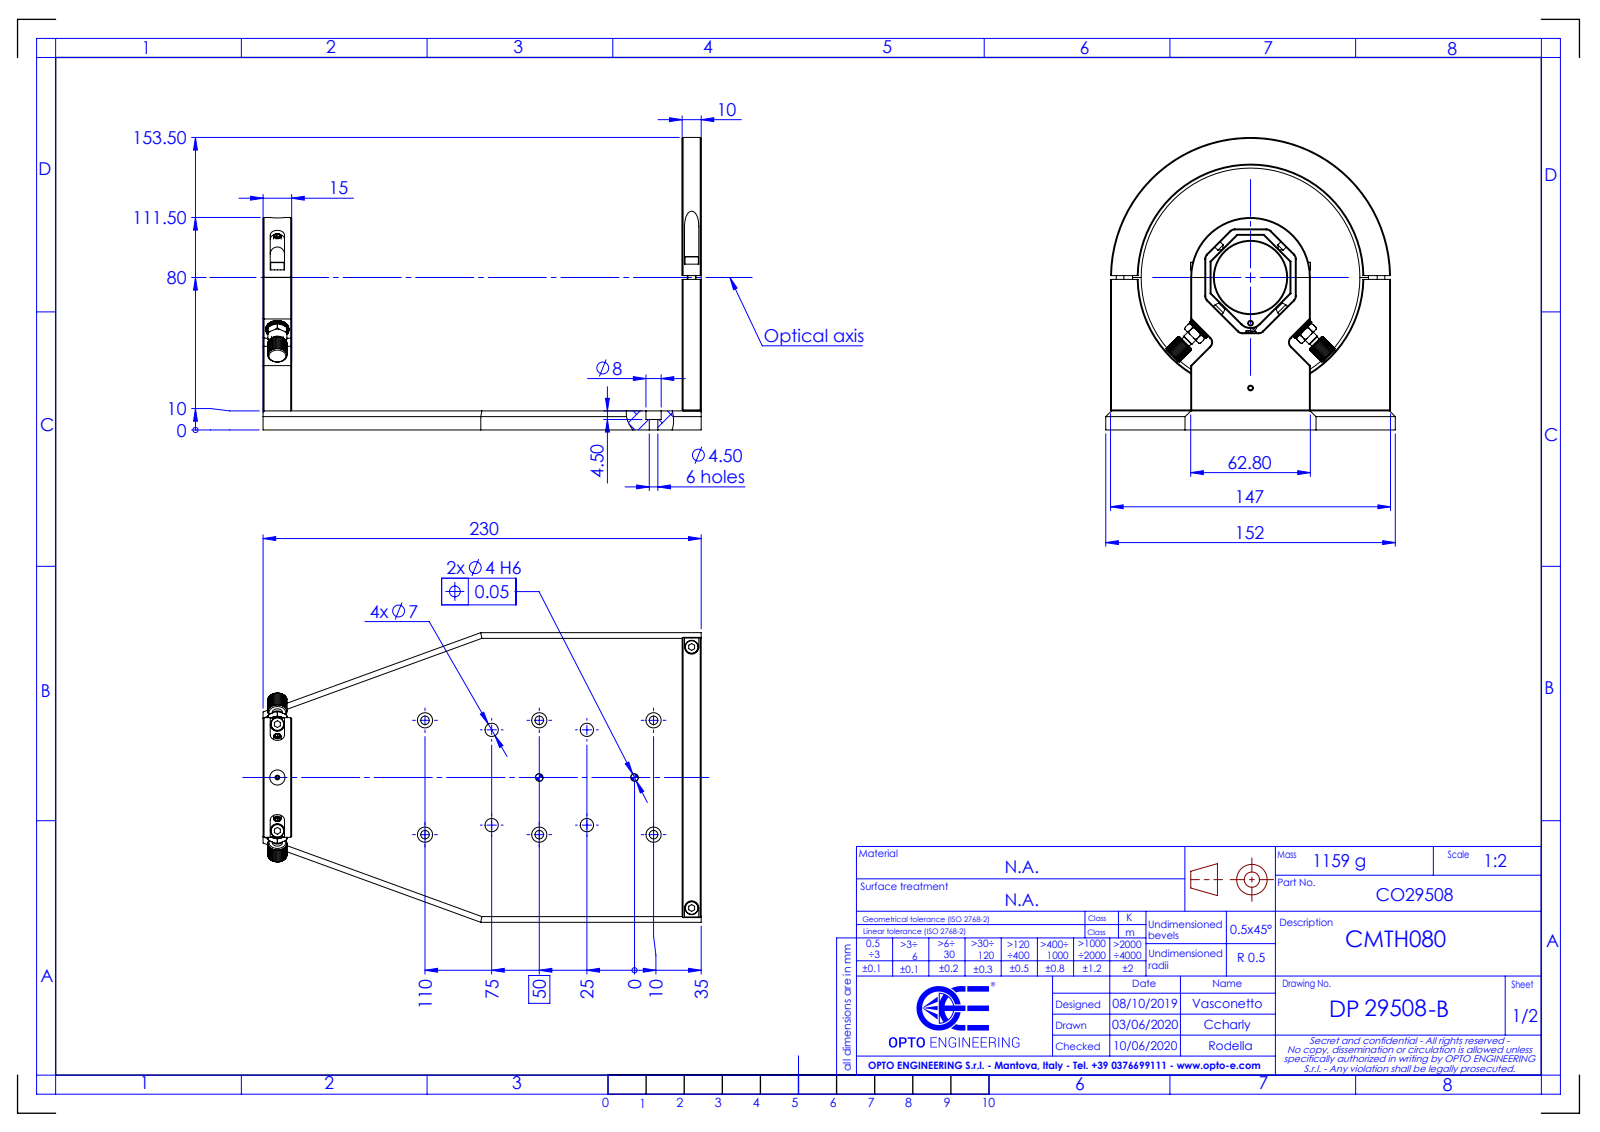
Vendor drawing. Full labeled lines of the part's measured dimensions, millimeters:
Part name (STEP PRODUCT): DP29508
STEP written by: SolidWorks 2021 (CONFIG_CONTROL_DESIGN)
Units: millimetres
Bodies: 0 solids, 710 faces (418 planar, 160 cylindrical, 132 other)
Overall size (bounding box): 230 × 153.5 × 152
Round holes (diameter × count): ⌀8 ×11, ⌀4.5 ×6, ⌀7 ×4, ⌀3 ×2, ⌀4 ×2, ⌀2.5 ×1, ⌀10.5 ×1, ⌀38 ×1, ⌀118 ×1
Round bosses / shafts (diameter × count): ⌀7 ×5, ⌀6 ×2, ⌀5.4 ×2, ⌀4 ×2
Partial cylindrical surfaces — rounded edges, fillets, slot ends (radius × count): R0.1 ×16, R3 ×10, R3.75 ×6, R6 ×2, R7 ×1, R31.4 ×1, R61.92 ×1, R73.5 ×1
Main face-to-face distances: 10, 230, 220, 15, 215, 205, 2.33, 7.67, 2.5, 44.6
Hole centre spacings: 35.36, 60, 50, 25.5, 60.42, 65.19, 67.08, 84.85
